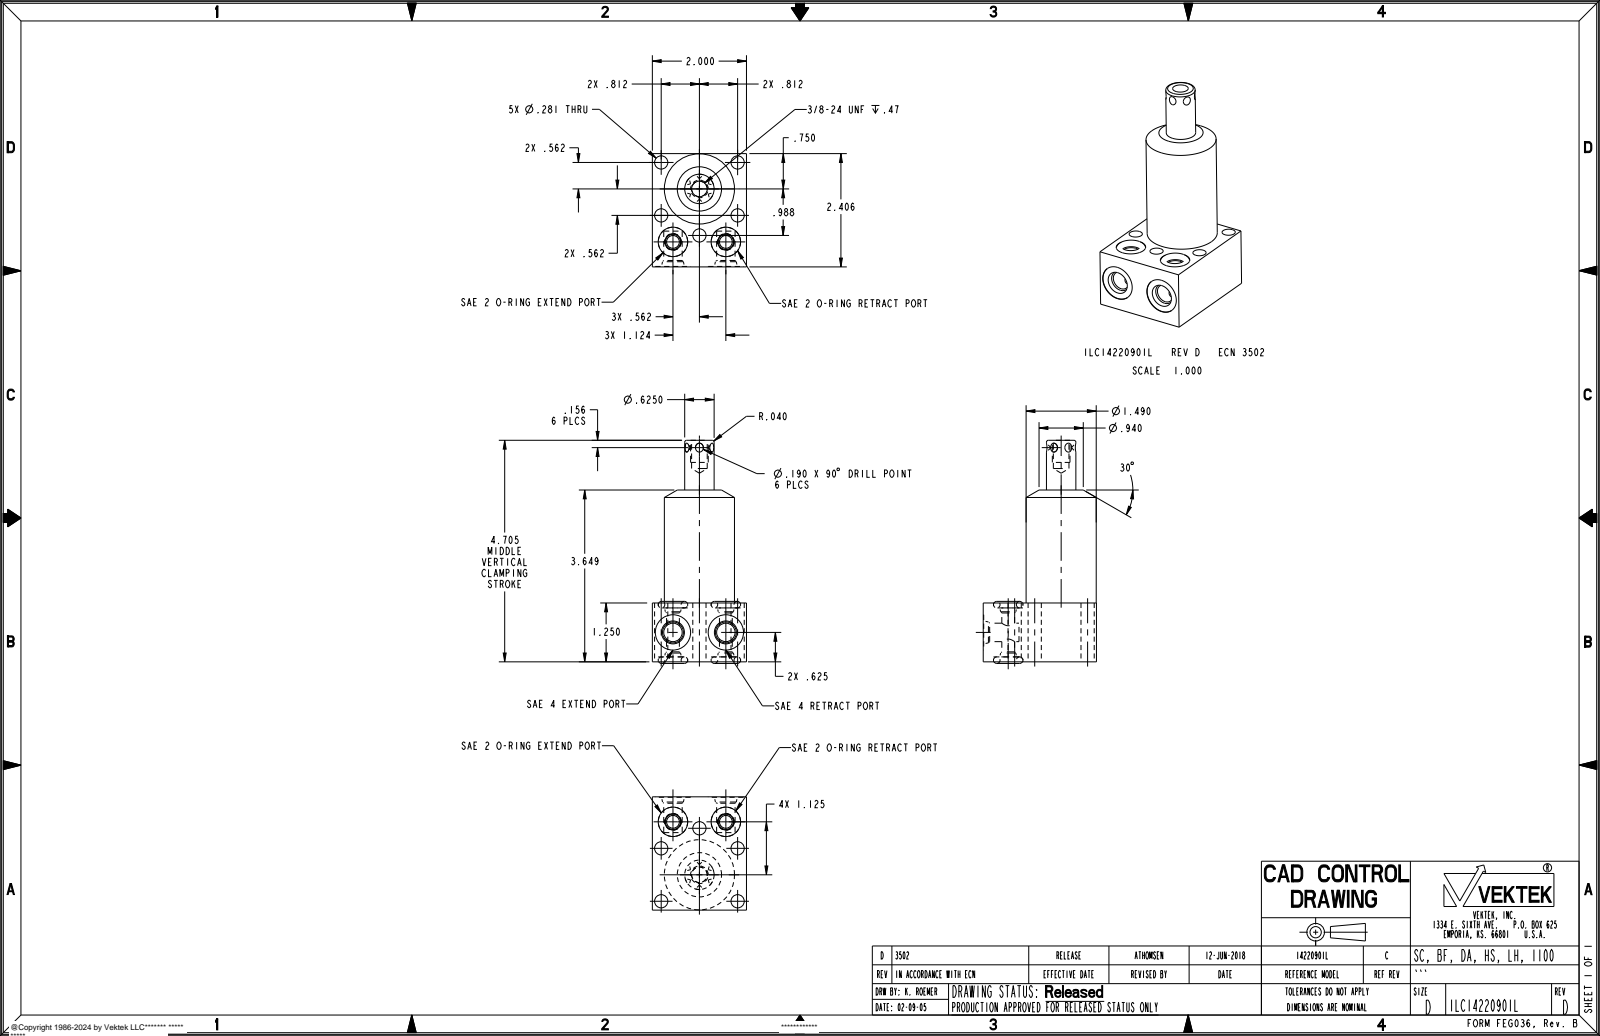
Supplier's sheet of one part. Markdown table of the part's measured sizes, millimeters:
| quantity | value |
| --- | --- |
| part name | ILC14220901L |
| STEP written by | PRO/ENGINEER BY PARAMETRIC TECHNOLOGY CORPORATION, 2013320 (AUTOMOTIVE_DESIGN) |
| units | millimeters |
| bodies | 5 solids, 117 faces (17 planar, 42 cylindrical, 58 other) |
| overall size | 120.4 × 61.1 × 50.8 |
| volume | 158 200 mm³ |
| surface area | 29 360 mm² |
| round holes (diameter × count) | 7.1 × 5, 6.9 × 2, 10 × 2, 15.9 × 2, 19.1 × 2, 8.4 × 1 |
| round bosses / shafts (diameter × count) | 37.8 × 1, 15.9 × 1, 9.5 × 1 |
| main face-to-face distances | 50.8, 31.8, 61.1, 2.7, 29.1, 60.9, 26.4, 92.7, 90, 63.6 |
| hole center spacings | 25.1, 28.5, 14.7, 15.6, 23.3, 31.9, 37.7, 41.2 |
